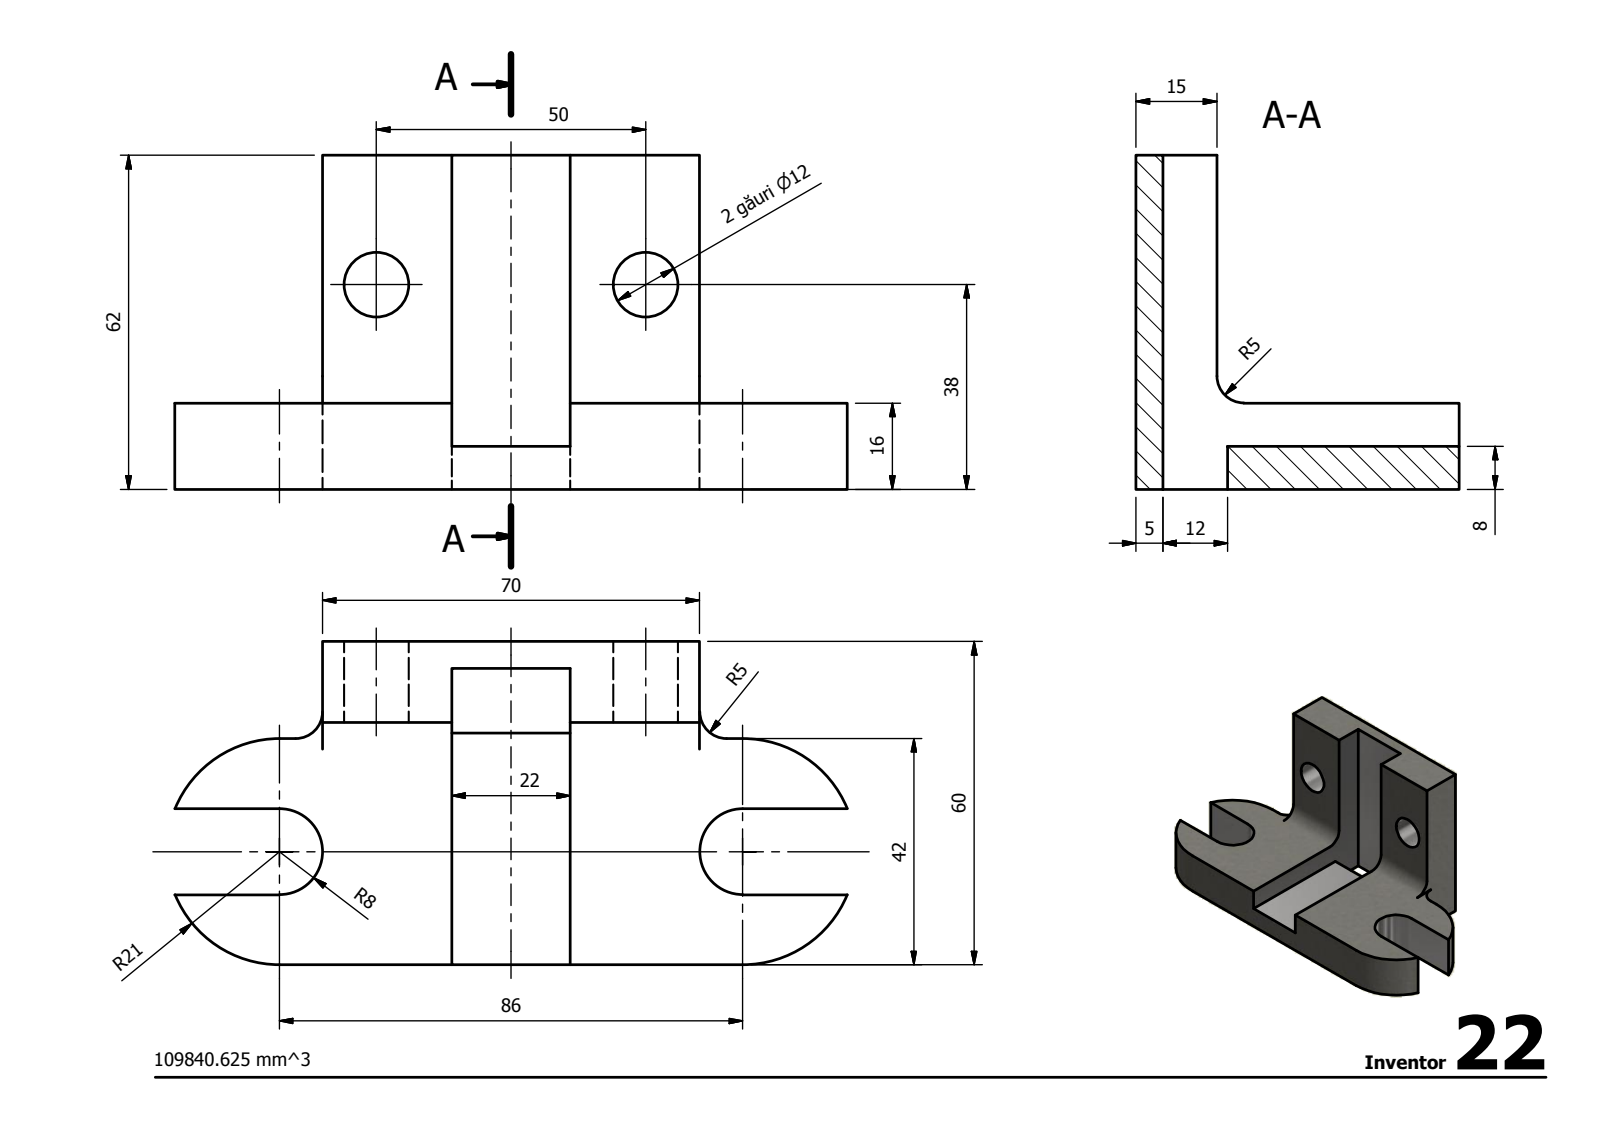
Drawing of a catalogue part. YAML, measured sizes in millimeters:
step_written_by: "Autodesk Inventor 2014 (AUTOMOTIVE_DESIGN)"
units: millimeters
bodies: {solids: 1, faces: 33, planar: 21, cylindrical: 12, other: 0}
overall_size: [124.83, 62, 60]
volume: 109840
surface_area: 27949
round_holes:
  - {diameter: 12, count: 2}
partial_cylinders:
  - {radius: 5, count: 3}
  - {radius: 8, count: 2}
  - {radius: 21, count: 2}
face_to_face_distances: [16, 46, 8, 24, 15, 10, 5, 45, 55, 60]
hole_center_spacings: [50]
